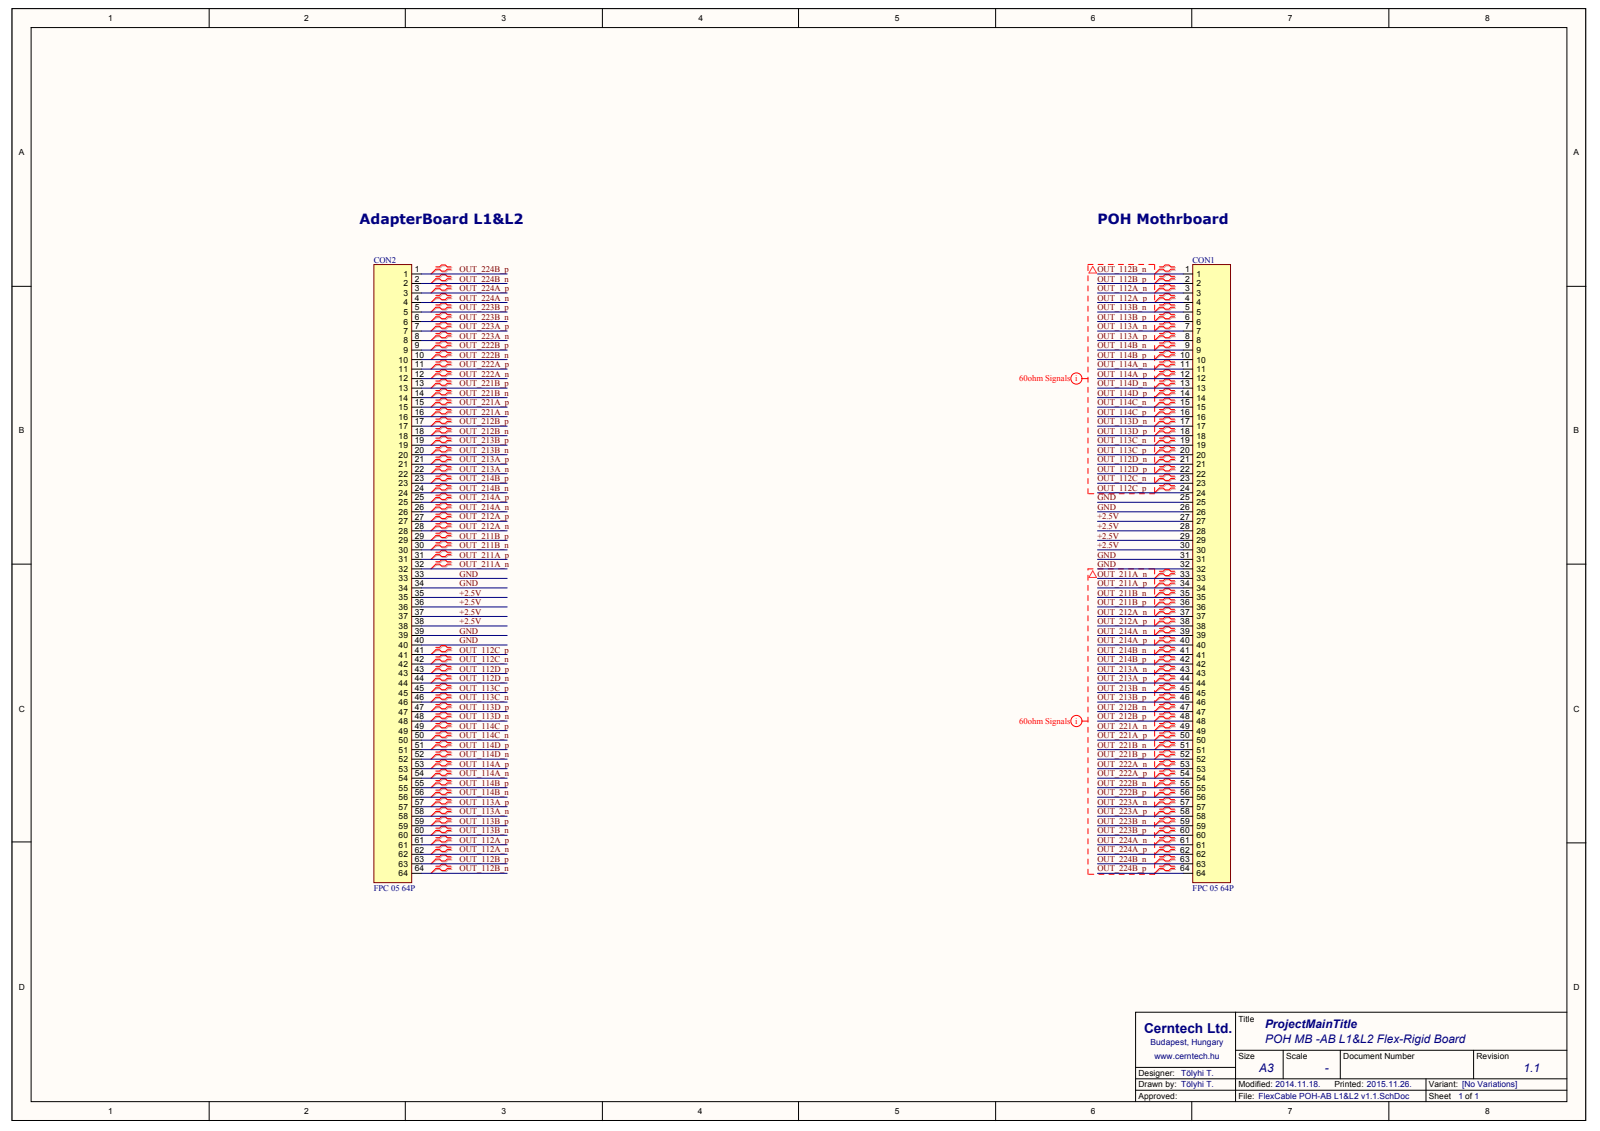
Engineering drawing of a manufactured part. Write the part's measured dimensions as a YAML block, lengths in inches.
part_name: "PCB; BoardFC_POH_L1&L2_v1.1.3"
step_written_by: "Open CASCADE 6.5 (AUTOMOTIVE_DESIGN)"
units: inches
bodies: {solids: 16, faces: 177, planar: 177, cylindrical: 0, other: 0}
overall_size: [5.63, 1.323, 0.009]
volume: 0.039
surface_area: 14.72
face_to_face_distances: [0.197, 1.28, 0.062, 0.031, 0.157, 3.791, 3.729, 1.642, 1.704, 5.433]
